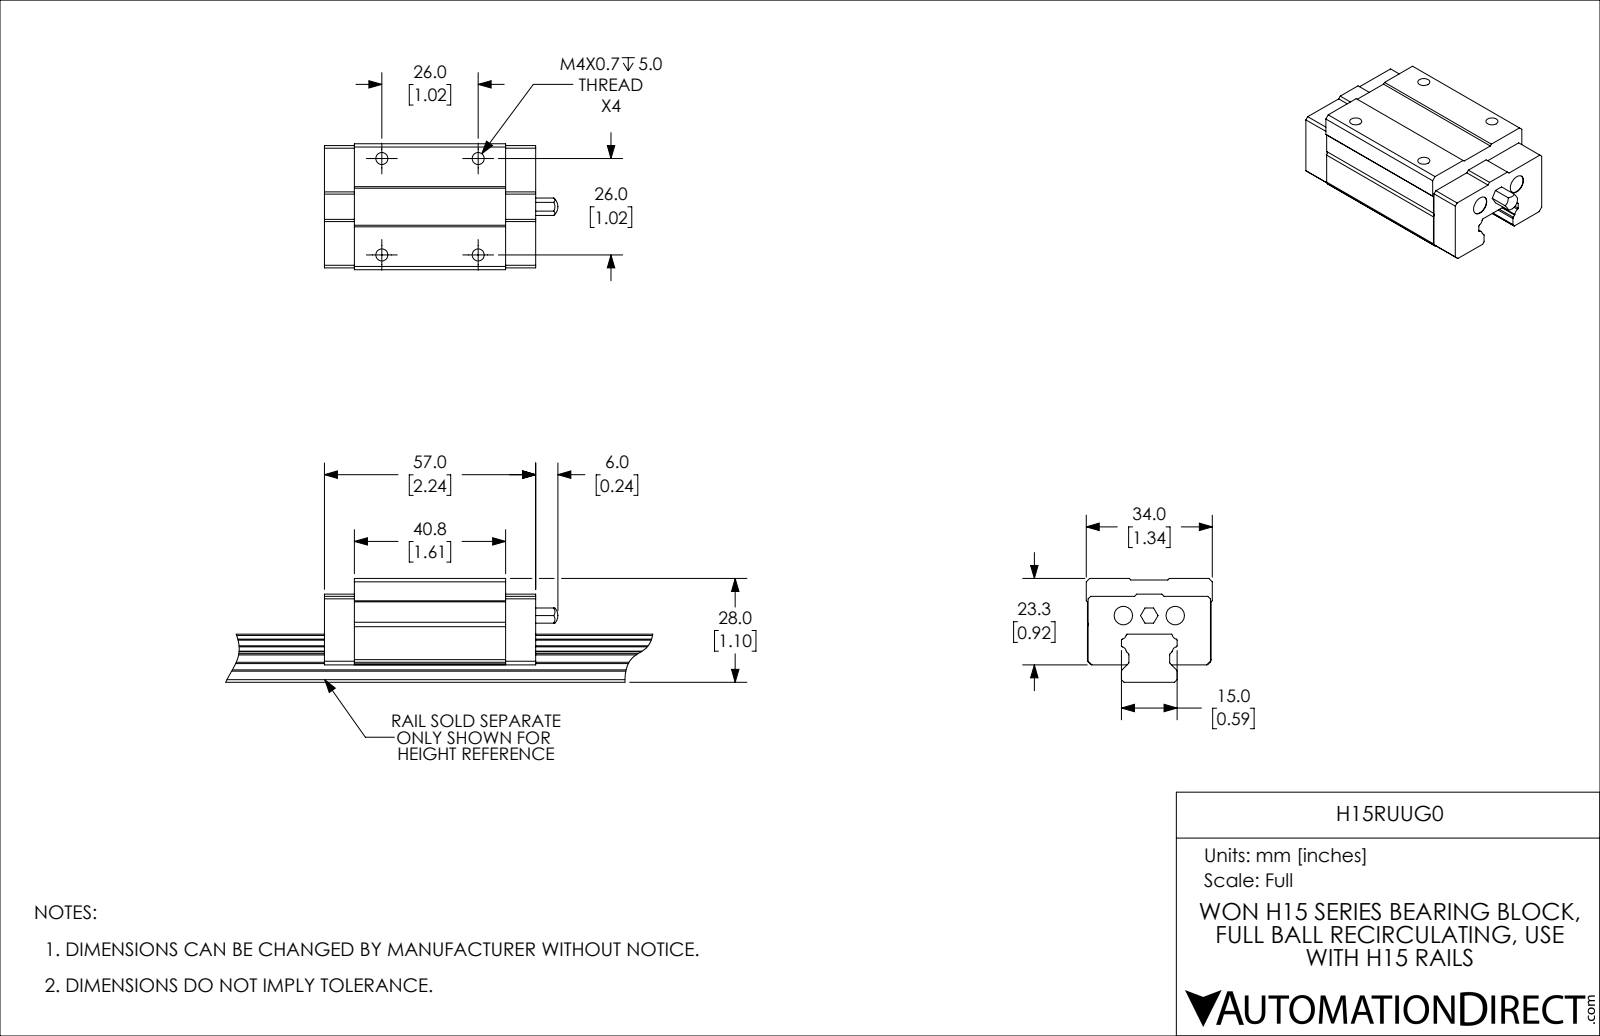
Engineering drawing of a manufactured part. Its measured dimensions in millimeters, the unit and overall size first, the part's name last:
Units: millimetres
Overall size (bounding box): 63 × 34 × 23.3
Round holes (diameter × count): ⌀3.24 ×5, ⌀5 ×2
Round bosses / shafts (diameter × count): ⌀4 ×1
Partial cylindrical surfaces — rounded edges, fillets, slot ends (radius × count): R0.3 ×6, R1 ×5, R0.5 ×4, R1.4 ×4, R0.6 ×2
Main face-to-face distances: 23.3, 15, 8.3, 33.4, 33.2, 57, 0.5, 33.5, 33.7, 22.9
Hole centre spacings: 26, 7, 36.77, 14
Volume: 35 453 mm³ · Surface area: 9 161 mm²
Bodies: 2 solids, 124 faces (67 planar, 45 cylindrical, 12 other)
Part name (STEP PRODUCT): H15RUUG0
STEP written by: SolidWorks 2019 (CONFIG_CONTROL_DESIGN)
